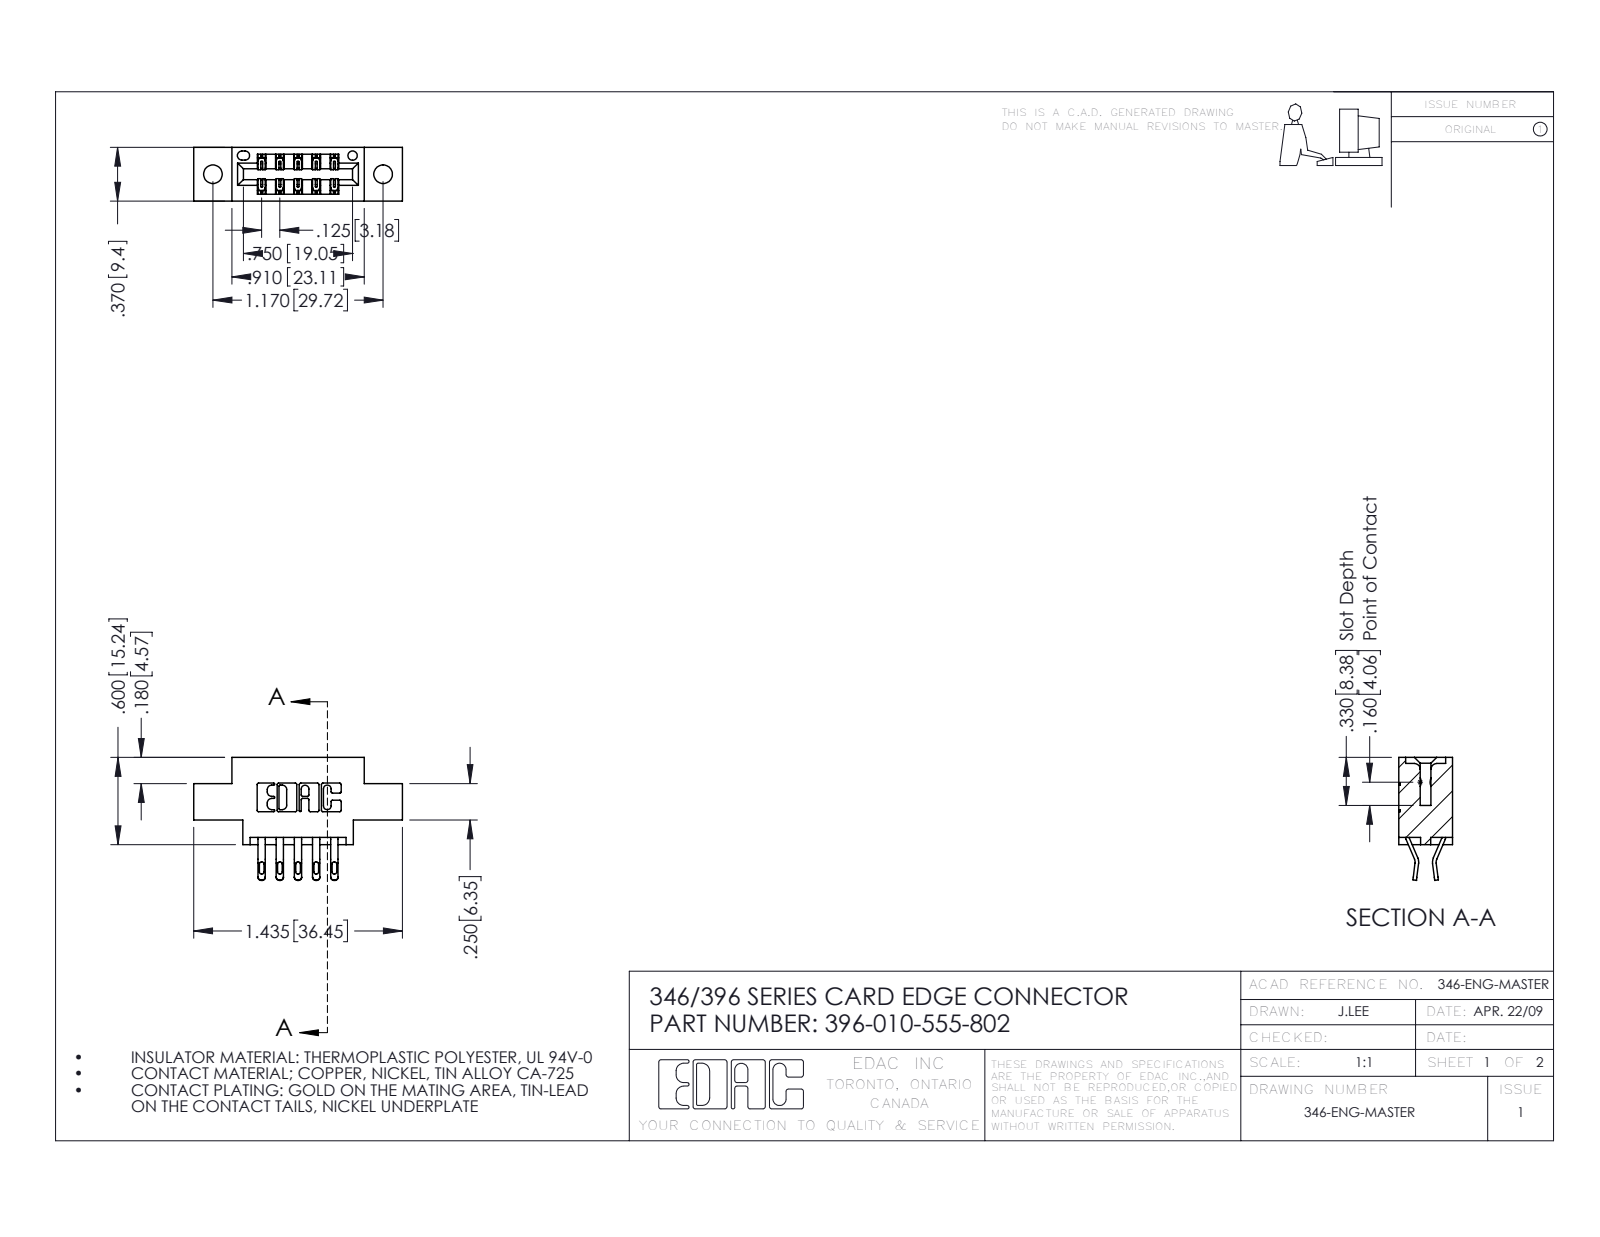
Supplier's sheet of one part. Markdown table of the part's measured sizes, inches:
| quantity | value |
| --- | --- |
| part name | 345-292-001_555 Tail; 346 Part_0.170 Offset - 0.128 Dia; 396-010-555-802 |
| STEP written by | SolidWorks 2016 (CONFIG_CONTROL_DESIGN) |
| units | inches |
| bodies | 11 solids, 706 faces (410 planar, 296 cylindrical, 0 other) |
| overall size | 1.435 × 0.845 × 0.37 |
| volume | 0.189 in³ |
| surface area | 5.734 in² |
| round holes (diameter × count) | 0.128 × 2, 0.064 × 1 |
| partial cylindrical surfaces (radius × count) | 0.01 × 22, 0.016 × 20, 0.02 × 20, 0.006 × 15, 0.007 × 6, 0.031 × 6, 0.026 × 3, 0.01 × 2 |
| main face-to-face distances | 0.37, 0.25, 0.048, 0.322, 0.125, 0.148, 0.222, 0.1, 0.174, 0.025 |
| hole center spacings | 0.246, 0.969, 1.17 |
